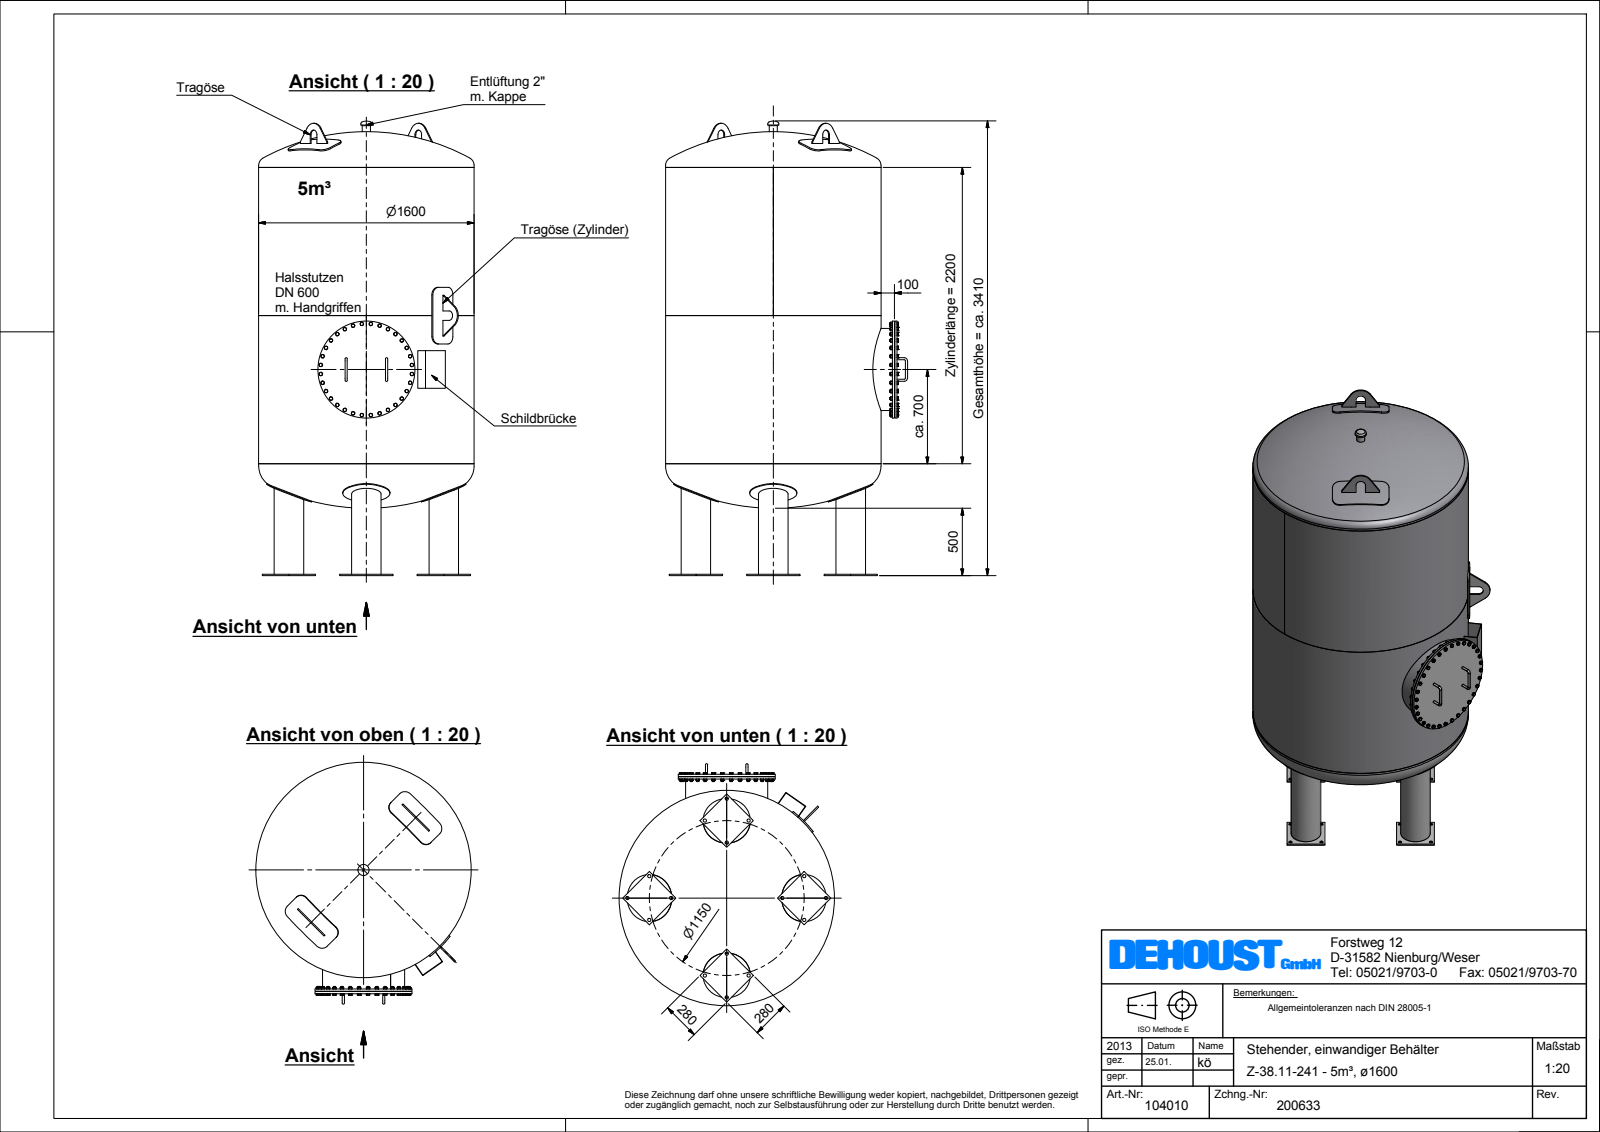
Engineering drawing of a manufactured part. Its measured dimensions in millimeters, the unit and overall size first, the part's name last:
Units: millimetres
Overall size (bounding box): 3375.54 × 1797 × 1600
Round holes (diameter × count): ⌀209.1 ×4, ⌀598 ×1, ⌀1590 ×1
Round bosses / shafts (diameter × count): ⌀16 ×38, ⌀22.5 ×32, ⌀350 ×4, ⌀219.1 ×4, ⌀1600 ×1, ⌀720 ×1, ⌀660 ×1, ⌀610 ×1
Partial cylindrical surfaces — rounded edges, fillets, slot ends (radius × count): R56 ×12, R35 ×3, R85 ×3, R810 ×1
Main face-to-face distances: 35, 10, 830.07, 820.07, 16, 19, 3, 2.93, 549.42, 559.42
Hole centre spacings: 575, 813.17, 1150
Volume: 545 800 000 mm³ · Surface area: 37 380 000 mm²
Bodies: 2 solids, 1075 faces (610 planar, 151 cylindrical, 314 other)
Part name (STEP PRODUCT): Beh\S\dlter_Z-38_11-241_1600_005_KV
STEP written by: Autodesk Inventor 2012 (AUTOMOTIVE_DESIGN)
